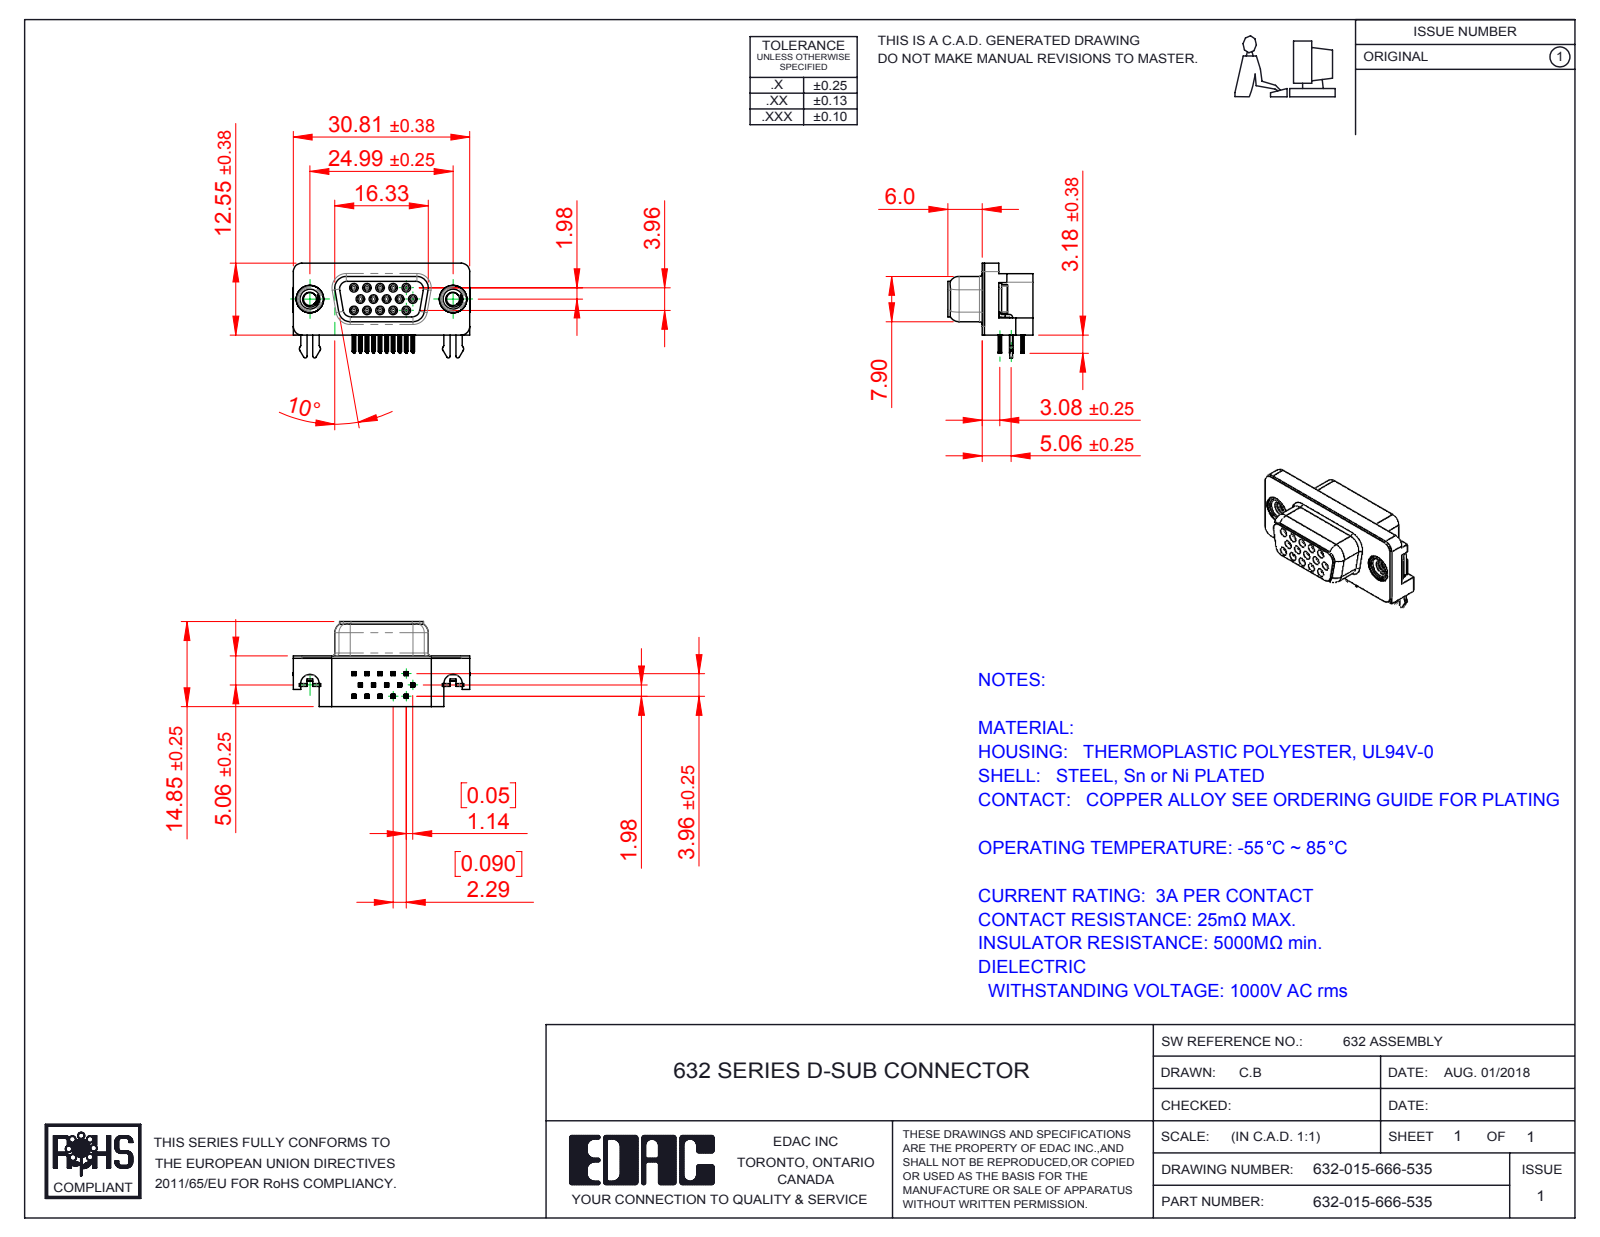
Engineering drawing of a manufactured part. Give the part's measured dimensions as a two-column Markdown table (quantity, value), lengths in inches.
| quantity | value |
| --- | --- |
| part name | 632 Contact Bottom; 632 4-40 Threaded Rivet; 632 2 Prong Board Lock; 632 Housing_15 Socket (+5 more) |
| STEP written by | SolidWorks 2016 (CONFIG_CONTROL_DESIGN) |
| units | inches |
| bodies | 23 solids, 2426 faces (1006 planar, 654 cylindrical, 766 other) |
| overall size | 1.216 × 0.652 × 0.585 |
| volume | 0.183 in³ |
| surface area | 8.28 in² |
| round holes (diameter × count) | 0.031 × 15, 0.035 × 15, 0.089 × 2, 0.098 × 2, 0.157 × 2, 0.189 × 2, 0.197 × 2 |
| round bosses / shafts (diameter × count) | 0.047 × 15, 0.193 × 2, 0.187 × 2, 0.154 × 2 |
| partial cylindrical surfaces (radius × count) | 0.004 × 120, 0.006 × 60, 0.014 × 30, 0.013 × 15, 0.039 × 11, 0.011 × 10, 0.02 × 10, 0.01 × 8 |
| main face-to-face distances | 0.016, 0.333, 0.348, 0.078, 0.114, 0.234, 0.098, 0.252, 0.264, 0.278 |
| hole center spacings | 0.09, 0.09, 0.156, 0.18, 0.238, 0.156, 0.18, 0.27 |
